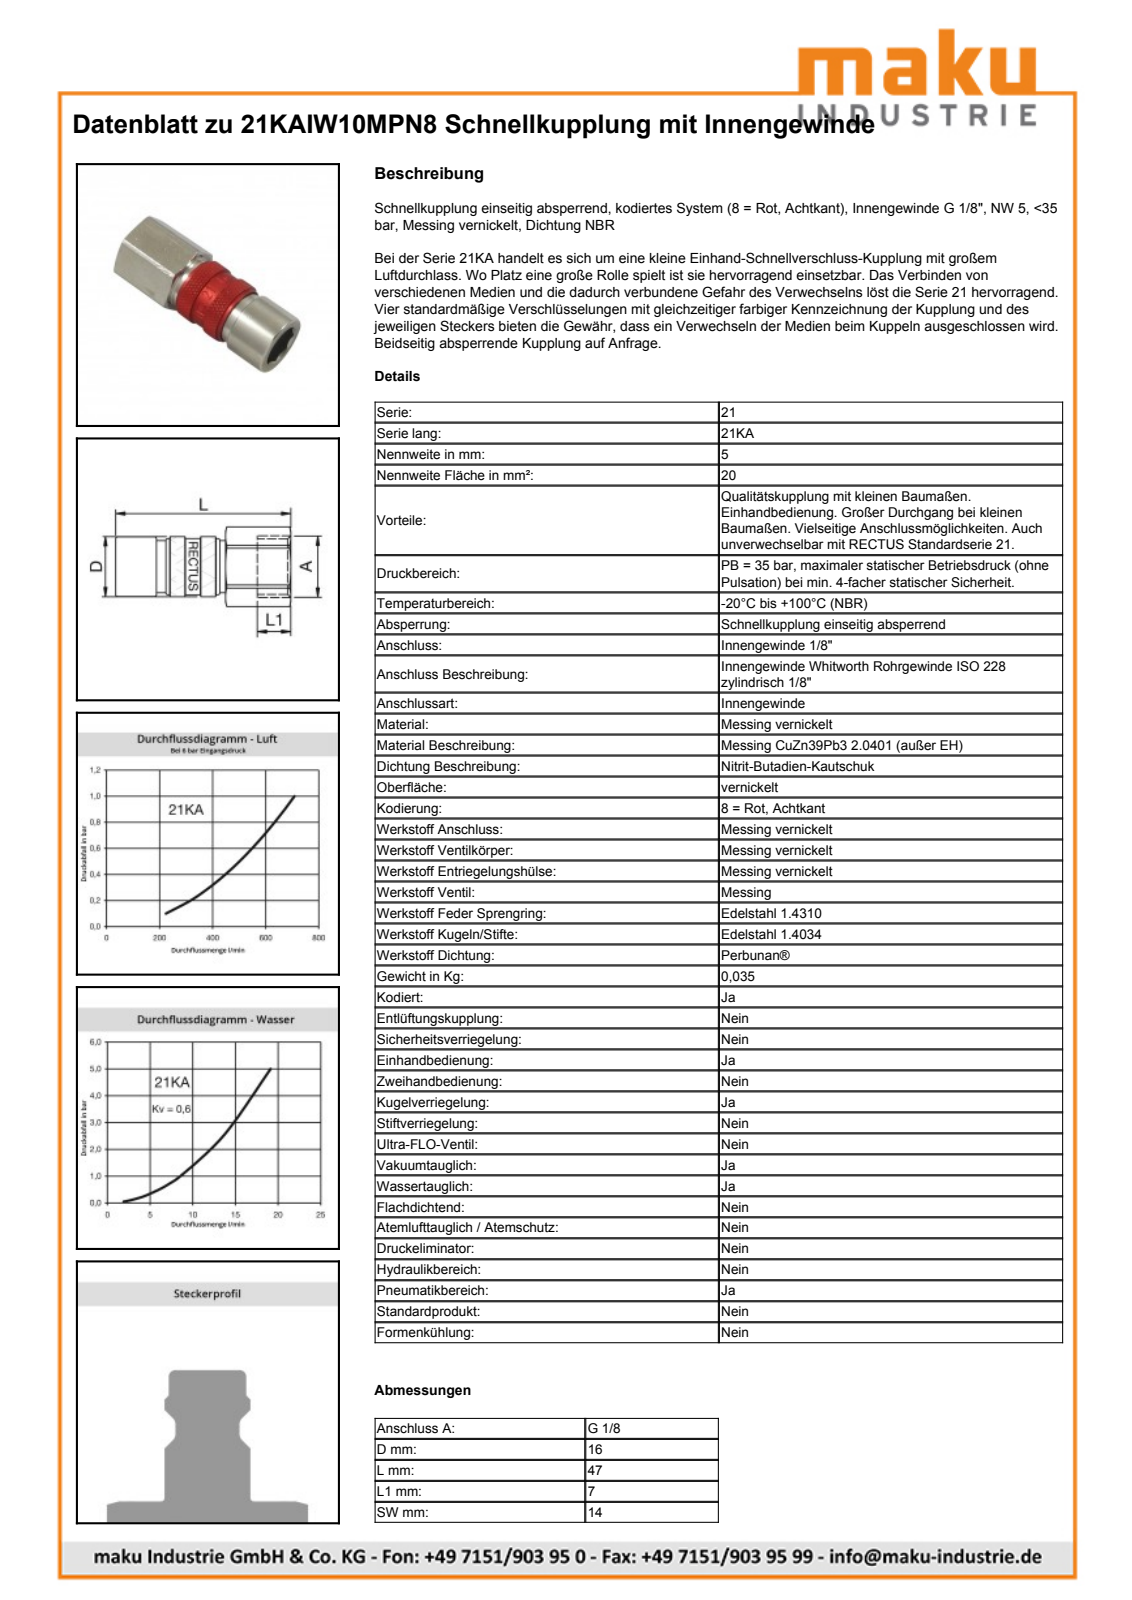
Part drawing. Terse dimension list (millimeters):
name: D108404
written by: Autodesk Inventor 2013 (AUTOMOTIVE_DESIGN)
unit: mm
bodies: 1 solid, 443 faces (170 planar, 63 cylindrical, 210 other)
size: 45.1 × 16.15 × 16.15
volume: 6 480 mm³; area: 4 484 mm²
holes: 1× ⌀8.57, 1× ⌀11.46, 1× ⌀12.1, 1× ⌀12.15, 1× ⌀14
bosses: 1× ⌀16.15, 1× ⌀15.8, 1× ⌀15.1, 1× ⌀12, 1× ⌀11.4, 1× ⌀11.06
rounds: 1× R7.45
face distances: 14, 10, 35.1, 45.1, 36.64, 26.64, 8.46, 15.1, 20, 25.1
